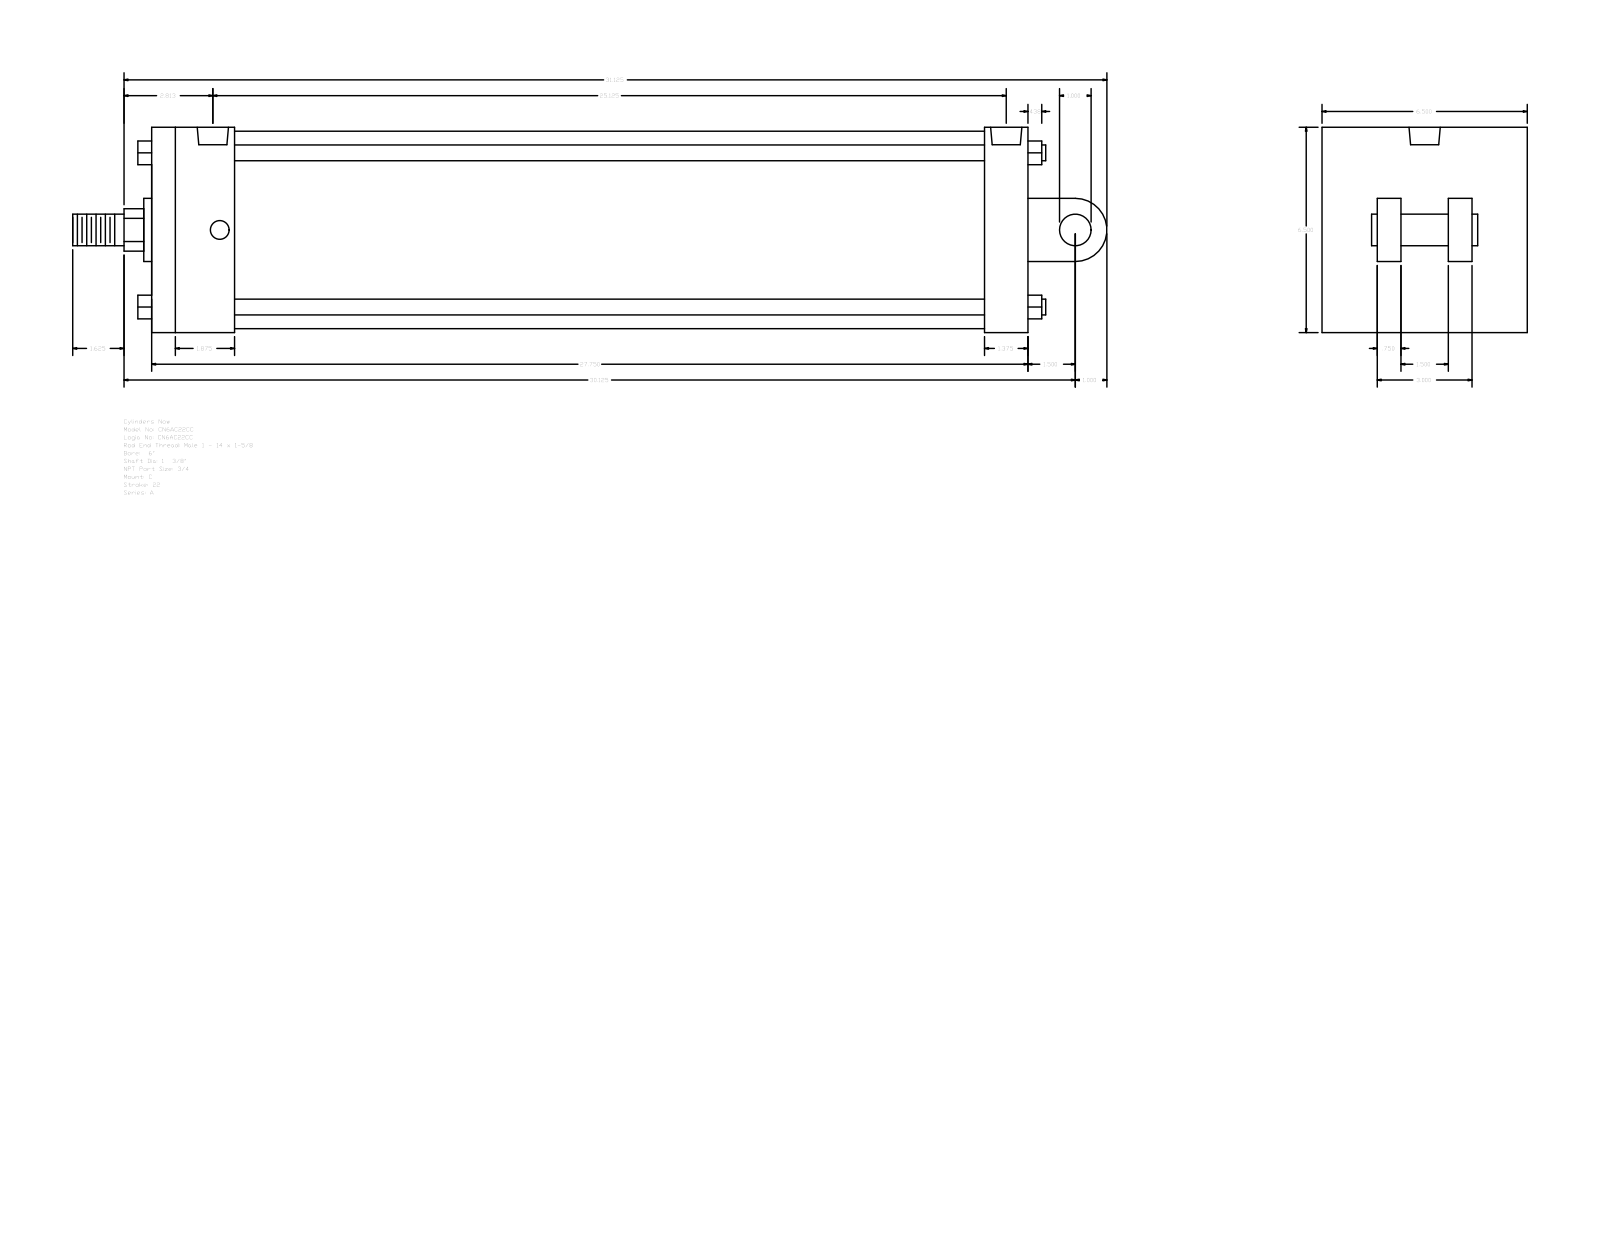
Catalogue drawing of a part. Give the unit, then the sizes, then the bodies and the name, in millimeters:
Units: millimetres
Overall size (bounding box): 831.85 × 165.1 × 165.1
Round holes (diameter × count): ⌀15.08 ×4, ⌀25.12 ×2
Round bosses / shafts (diameter × count): ⌀12.7 ×4, ⌀25.4 ×2, ⌀158.75 ×1, ⌀50.8 ×1, ⌀34.92 ×1
Partial cylindrical surfaces — rounded edges, fillets, slot ends (radius × count): R17.06 ×1, R25.4 ×1
Main face-to-face distances: 165.1, 704.85, 57.15, 19.05, 66.67, 638.18, 669.92, 603.25, 34.93, 63.5
Hole centre spacings: 5.56, 627.05, 632.61, 638.17
Bodies: 0 solids, 135 faces (102 planar, 33 cylindrical, 0 other)
Part name (STEP PRODUCT): A_C__0600_1.375
STEP written by: GSSL Pune (CONFIG_CONTROL_DESIGN)
